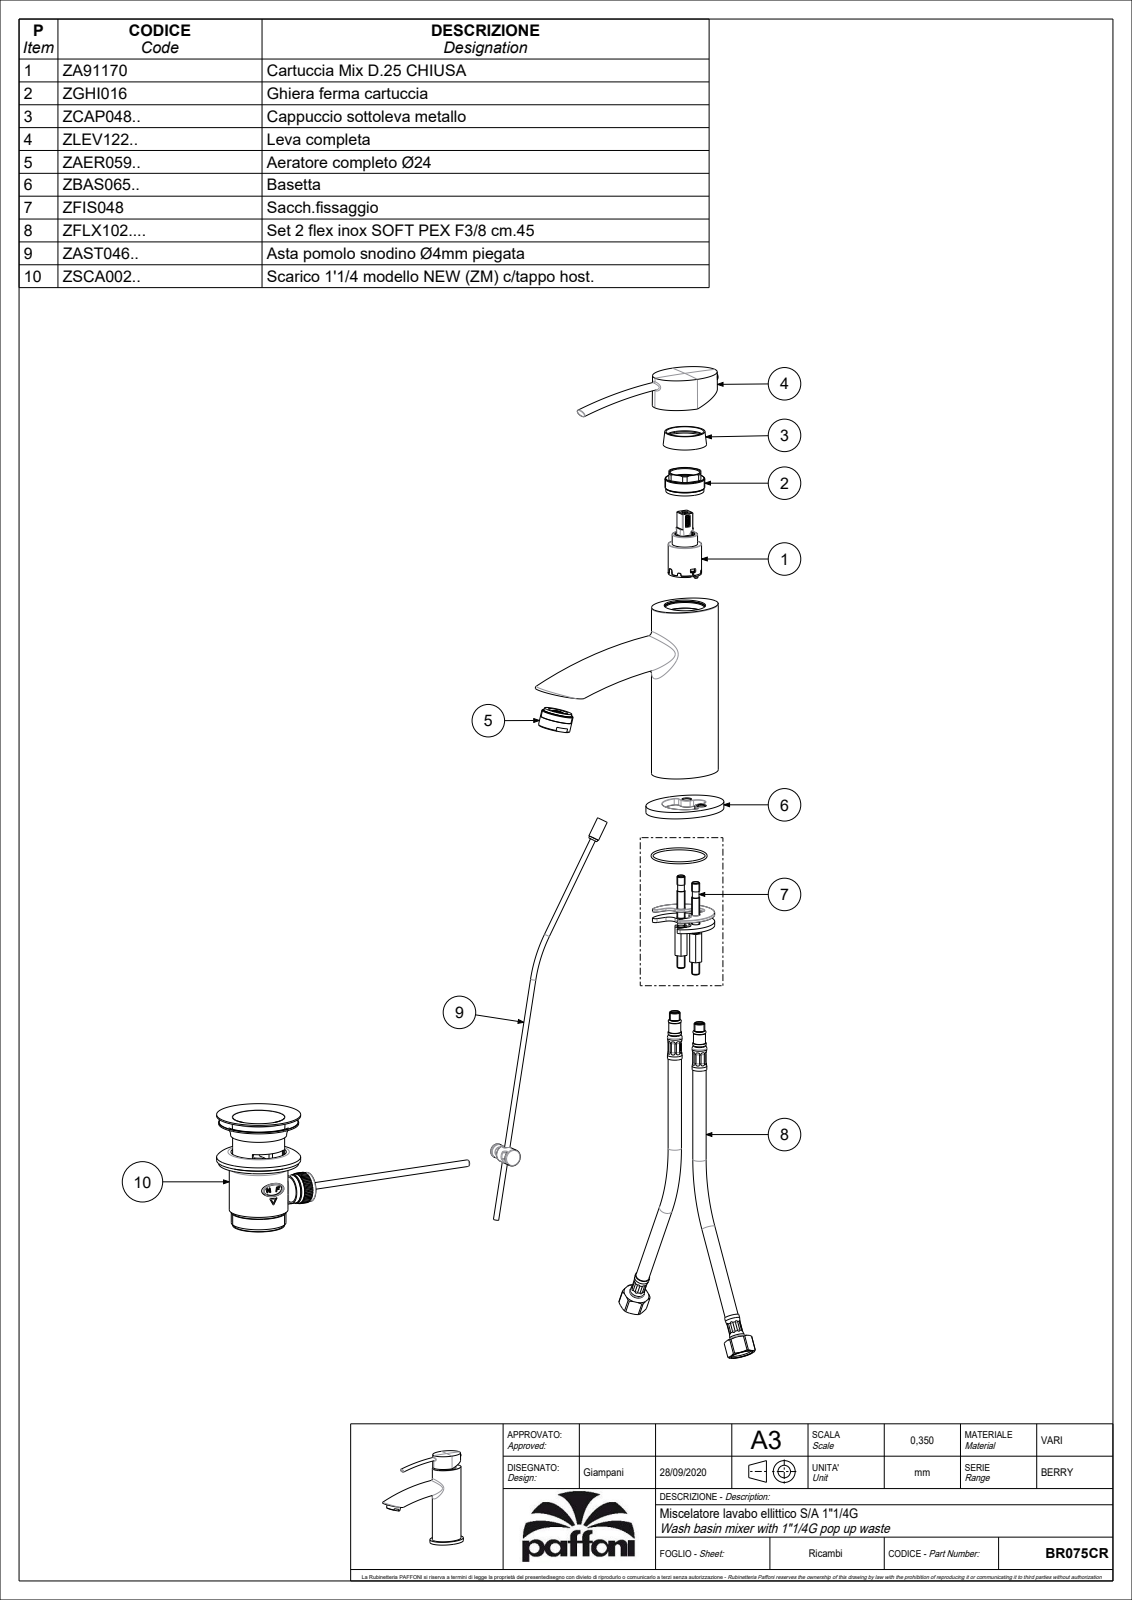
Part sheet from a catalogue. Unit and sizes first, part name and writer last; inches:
Units: inches
Overall size (bounding box): 6.776 × 6.268 × 1.811
Round holes (diameter × count): ⌀0.197 ×3, ⌀0.276 ×3, ⌀0.118 ×2, ⌀0.217 ×2, ⌀0.244 ×2, ⌀0.339 ×2, ⌀0.37 ×2, ⌀0.787 ×2, ⌀0.177 ×1, ⌀0.209 ×1, ⌀0.591 ×1, ⌀0.63 ×1
Round bosses / shafts (diameter × count): ⌀0.157 ×2, ⌀1.528 ×1, ⌀1.13 ×1, ⌀1.122 ×1, ⌀1.063 ×1, ⌀1.024 ×1, ⌀0.984 ×1, ⌀0.953 ×1
Partial cylindrical surfaces — rounded edges, fillets, slot ends (radius × count): R0.02 ×40, R0.012 ×23, R0.039 ×16, R0.008 ×13, R0.006 ×10, R0.079 ×10, R0.059 ×8, R0.049 ×4
Main face-to-face distances: 0.197, 6.177, 3.563, 5.98, 0.039, 4.035, 0.902, 5.276, 5.079, 0.472
Hole centre spacings: 0.295, 0.433, 0.443, 0.449, 0.53, 0.535, 0.546, 0.831
Volume: 9.256 in³ · Surface area: 138 in²
Bodies: 4 solids, 2626 faces (1945 planar, 329 cylindrical, 352 other)
Part name (STEP PRODUCT): BR075CR
STEP written by: CREO PARAMETRIC BY PTC INC, 2020044 (CONFIG_CONTROL_DESIGN)
